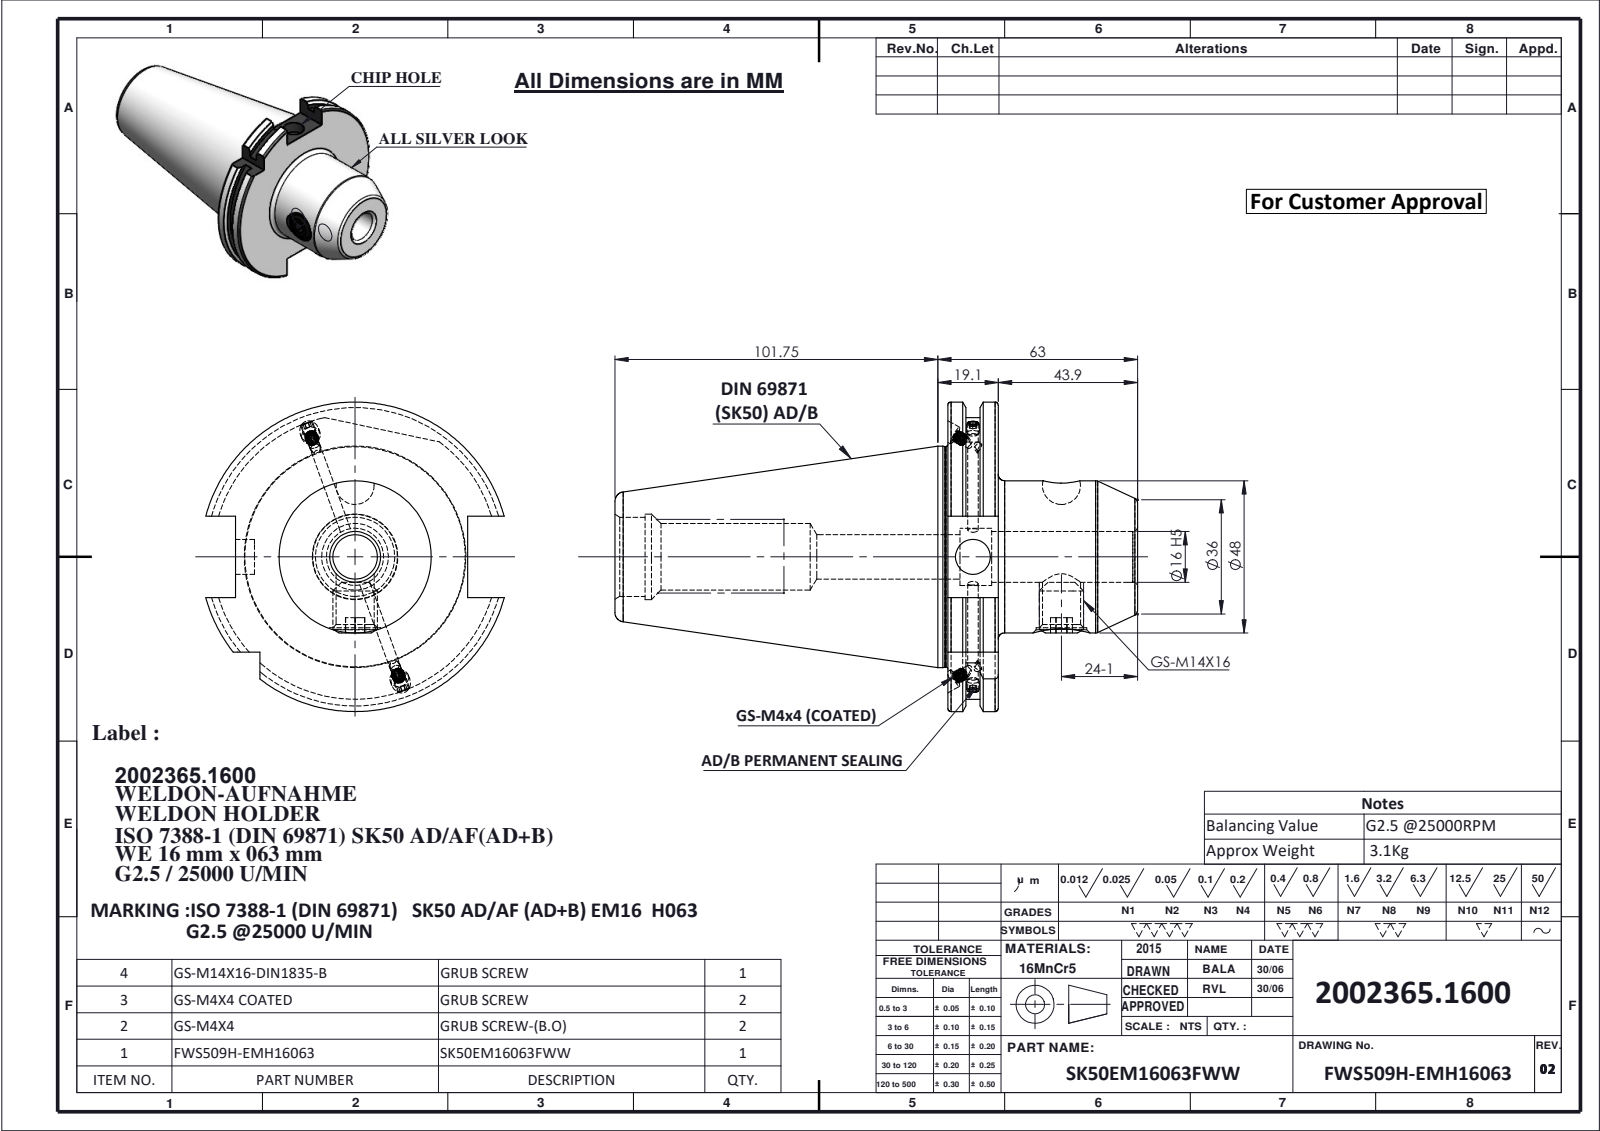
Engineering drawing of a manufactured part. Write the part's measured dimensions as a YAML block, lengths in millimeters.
part_name: "GS-M4X4-COATING_DIN 913 - M4 x 4-N; SK40EM16063FWW; GS-M14X16-DIN1835-B_ISO 4026 - M12 x 12-N; FWS509H-EMH16063 (+1 more)"
step_written_by: "SolidWorks 2024 (CONFIG_CONTROL_DESIGN)"
units: millimeters
bodies: {solids: 6, faces: 279, planar: 73, cylindrical: 81, other: 125}
overall_size: [164.75, 97.5, 94.05]
volume: 393092
surface_area: 53713
round_holes:
  - {diameter: 3.2, count: 2}
  - {diameter: 6, count: 2}
  - {diameter: 16, count: 2}
  - {diameter: 3.3, count: 1}
  - {diameter: 11, count: 1}
  - {diameter: 12, count: 1}
  - {diameter: 14, count: 1}
  - {diameter: 18, count: 1}
  - {diameter: 21, count: 1}
  - {diameter: 25, count: 1}
  - {diameter: 27, count: 1}
round_bosses_or_shafts:
  - {diameter: 4, count: 4}
  - {diameter: 2.9, count: 2}
  - {diameter: 69.85, count: 1}
  - {diameter: 69.45, count: 1}
  - {diameter: 48, count: 1}
  - {diameter: 14, count: 1}
partial_cylinders:
  - {radius: 44.9, count: 1}
  - {radius: 48.75, count: 1}
face_to_face_distances: [15.9, 59.8, 43.9, 5.65, 10.25, 54.15, 10.14, 4.49, 5.76, 49.66]
